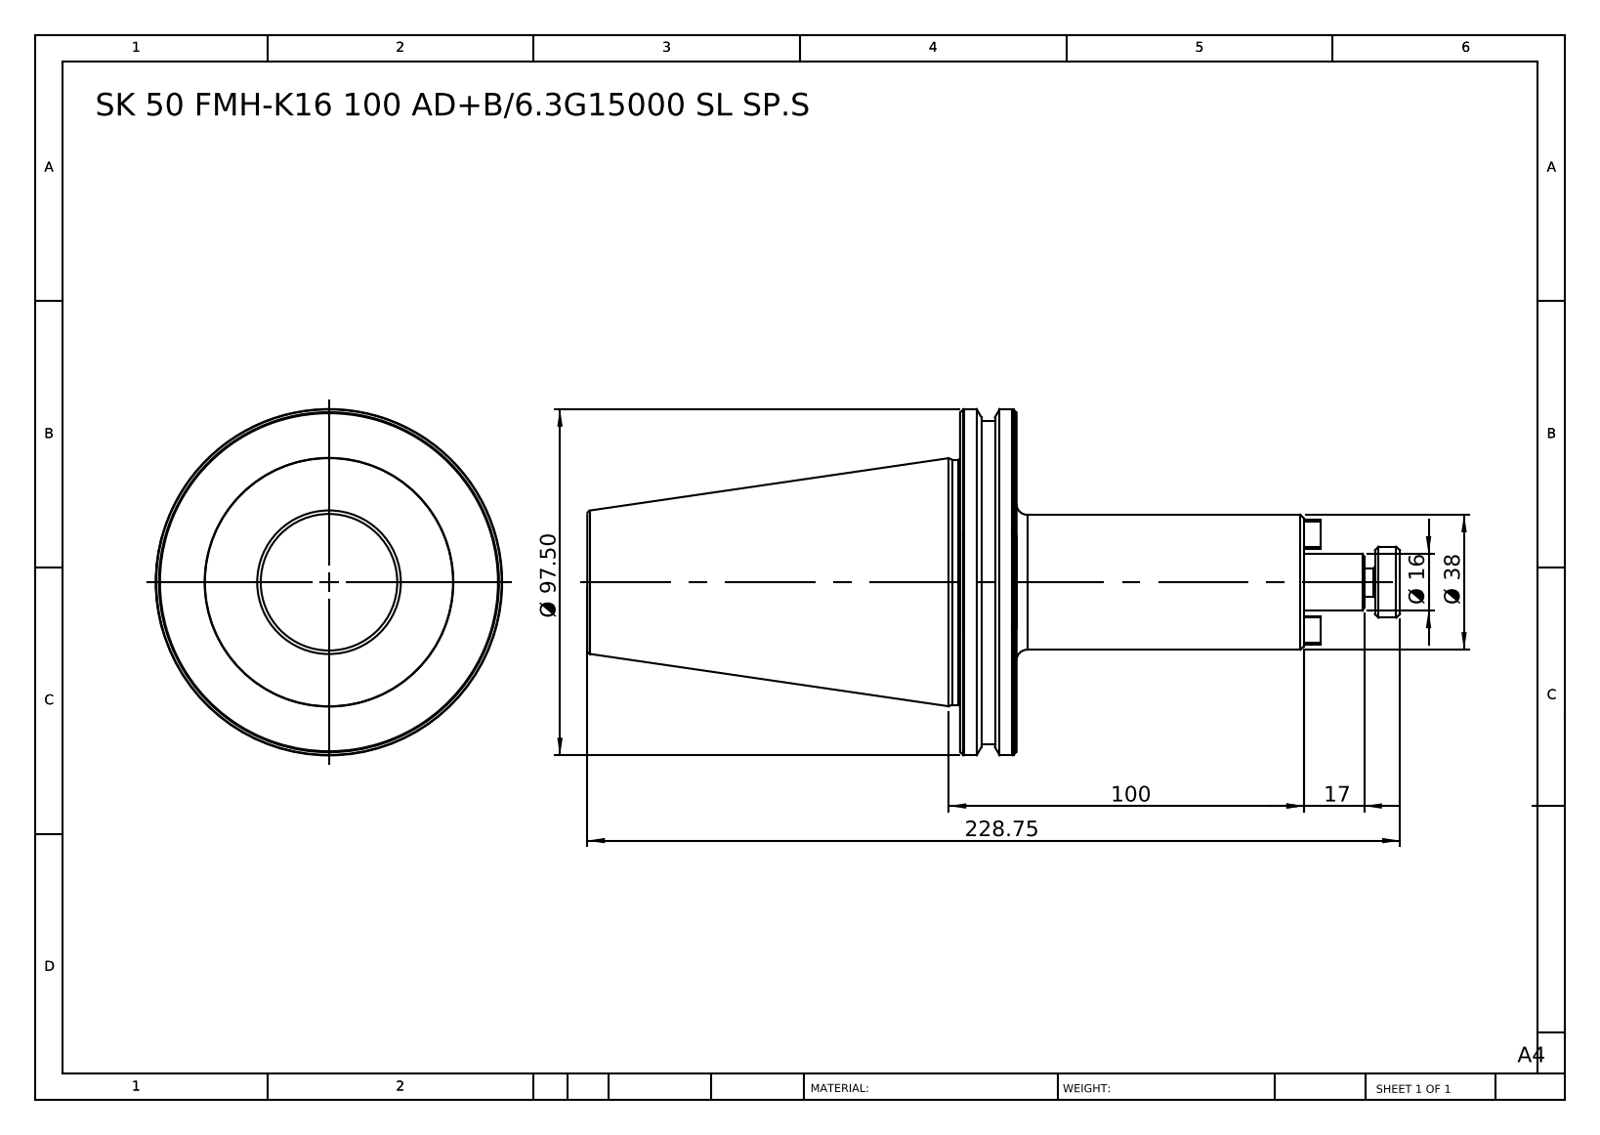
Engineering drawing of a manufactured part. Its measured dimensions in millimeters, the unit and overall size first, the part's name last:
Units: millimetres
Overall size (bounding box): 228.75 × 97.5 × 97.5
Round bosses / shafts (diameter × count): ⌀97.5 ×1, ⌀91 ×1, ⌀69 ×1, ⌀38 ×1, ⌀20 ×1, ⌀16 ×1, ⌀8 ×1
Main face-to-face distances: 15.9, 120.85, 104.95, 80.9, 96.8, 201.75, 27, 87, 6.1, 9.8
Volume: 471 767 mm³ · Surface area: 48 114 mm²
Bodies: 1 solid, 99 faces (27 planar, 16 cylindrical, 56 other)
Part name (STEP PRODUCT): SK50 FMH16 100 AD-6.3G15000 SL SP.S
STEP written by: SolidWorks 2014 (CONFIG_CONTROL_DESIGN)
